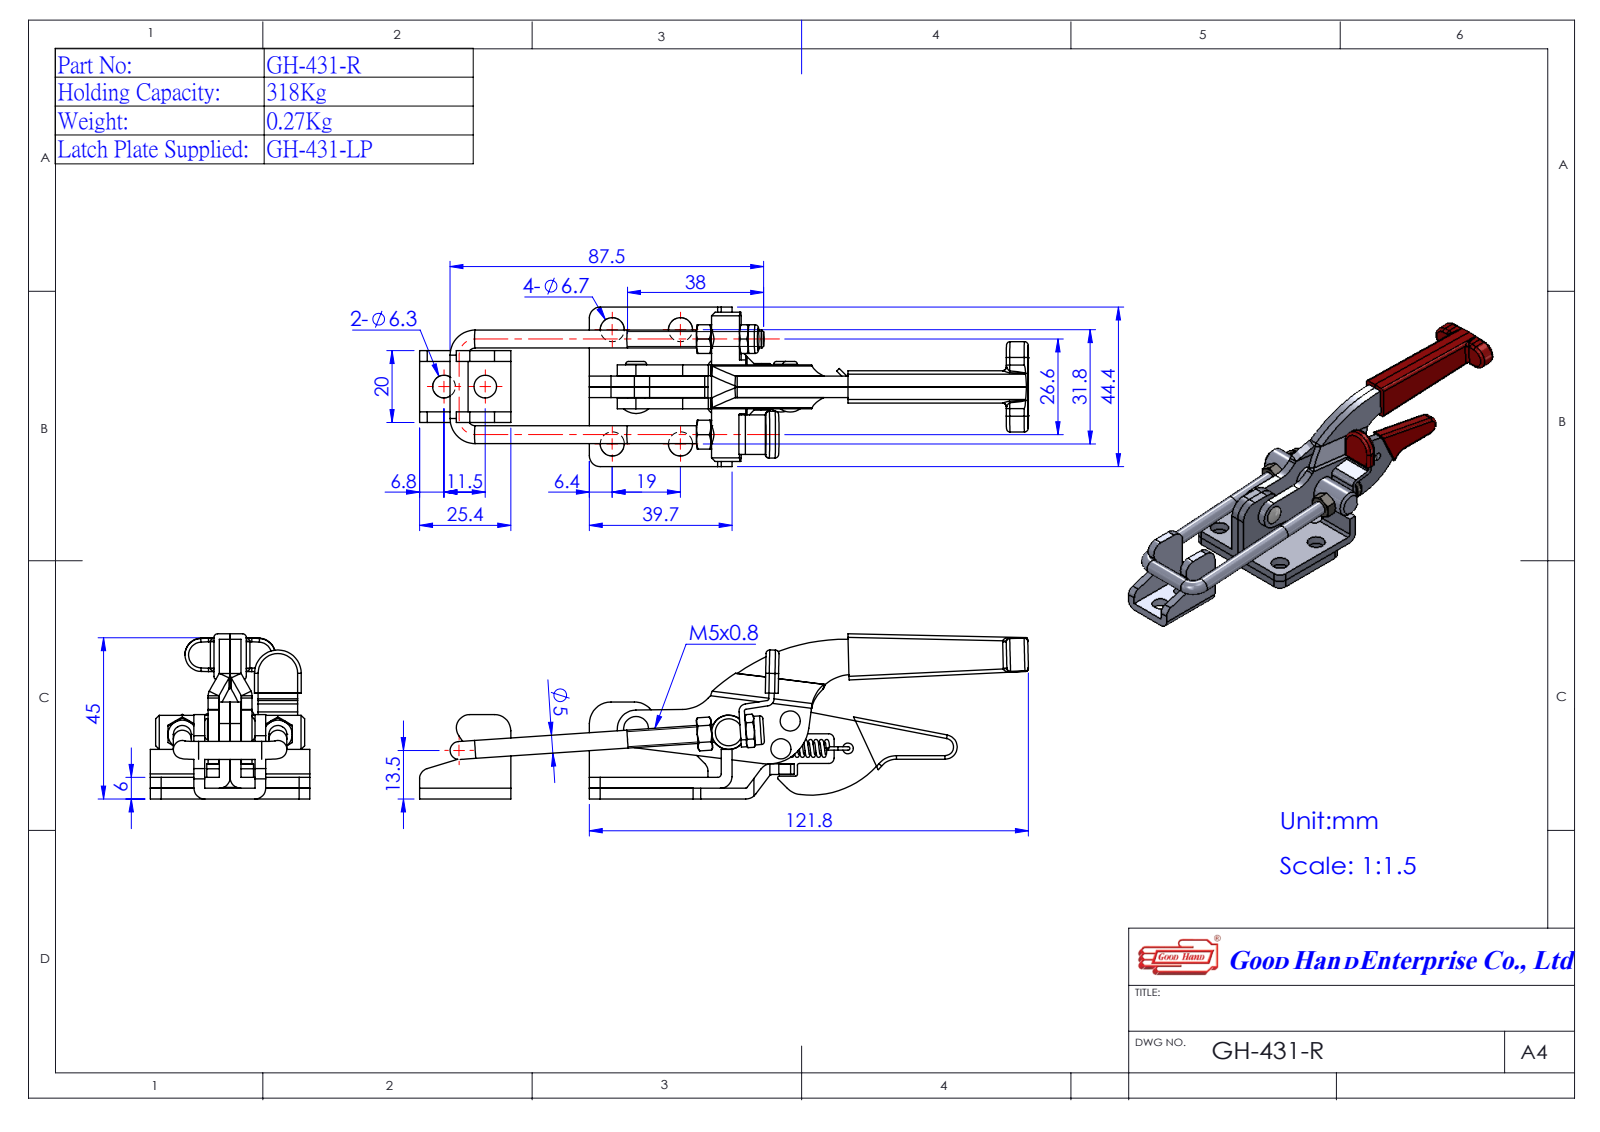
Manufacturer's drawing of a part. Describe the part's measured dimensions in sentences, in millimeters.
The part is named "Group2^GH-431-R(簡化); GH-431-R(簡化); Group3^GH-431-R(簡化); 443144-1^GH-431-R(簡化) (+2 more)". Its 3-D file was written by "SolidWorks 2016 (AUTOMOTIVE_DESIGN)". It is 7 solids with 450 faces: 177 planar, 174 cylindrical and 99 other. Overall it measures 169.56 by 45.96 by 44.4 millimeters. Its volume is 39 933 cubic millimeters and its surface area 26 233 square millimeters. Round holes: 4 of diameter 4.2, 4 of diameter 5, 4 of diameter 6.7, 2 of diameter 5.3, 2 of diameter 5.86, 2 of diameter 6.3, 1 of diameter 4, 1 of diameter 5.1, 1 of diameter 9.5. Round bosses or shafts: 3 of diameter 5, 2 of diameter 8, 1 of diameter 5.8, 1 of diameter 4, 1 of diameter 3. Partial cylindrical surfaces (rounded edges, fillets, slot ends): 7 of radius 0.5, 7 of radius 3, 5 of radius 11.5, 4 of radius 1, 4 of radius 2, 4 of radius 3.01, 4 of radius 52.32, 3 of radius 3.5. The main face-to-face distances are 3, 6, 1.5, 7.62, 1.62, 4.62, 6.12, 3.12, 9.12, 9.24. The hole center spacings are 26.6, 19, 31.8, 37.04, 11.5, 25.8, 38.73, 38.79.
